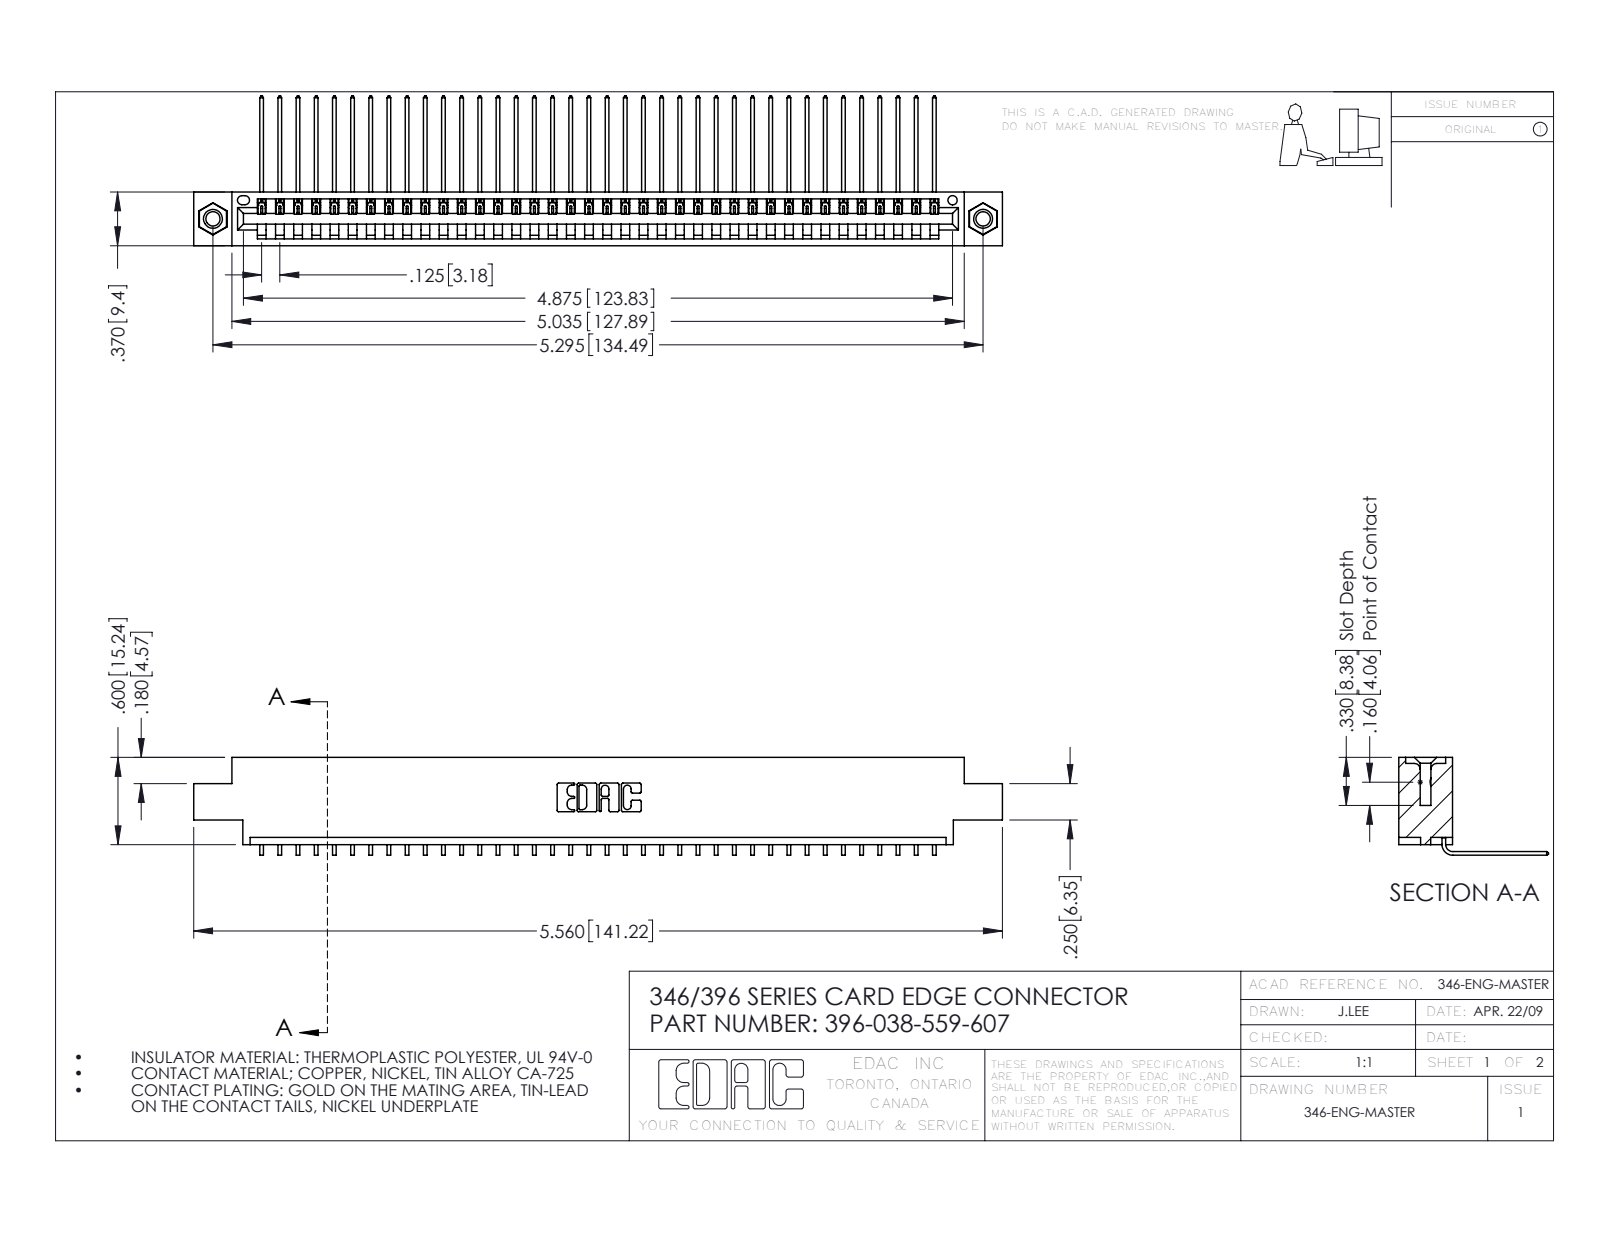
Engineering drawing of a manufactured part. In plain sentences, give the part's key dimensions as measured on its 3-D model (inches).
The part is named "346 Part_0.170 Offset - 0.156 Dia-TI; 396-038-559-607; 345-250-001_345-250-005-103; 345-292-001_558 559 Tail - 1". Its 3-D file was written by "SolidWorks 2016 (CONFIG_CONTROL_DESIGN)". It is 41 solids with 2466 faces: 1708 planar, 742 cylindrical and 16 other. Overall it measures 5.56 by 1.03 by 0.673 inches. Its volume is 0.821 cubic inches and its surface area 27.46 square inches. Round holes: 2 of diameter 0.098, 2 of diameter 0.125, 2 of diameter 0.156, 1 of diameter 0.064. Round bosses or shafts: 2 of diameter 0.155. Partial cylindrical surfaces (rounded edges, fillets, slot ends): 76 of radius 0.006, 22 of radius 0.01, 6 of radius 0.007, 6 of radius 0.031, 3 of radius 0.026, 2 of radius 0.031, 2 of radius 0.04, 1 of radius 0.014. The main face-to-face distances are 0.048, 0.322, 0.37, 0.025, 0.25, 0.072, 0.222, 0.148, 0.298, 0.1. The hole center spacings are 0.246, 5.086, 5.295.
